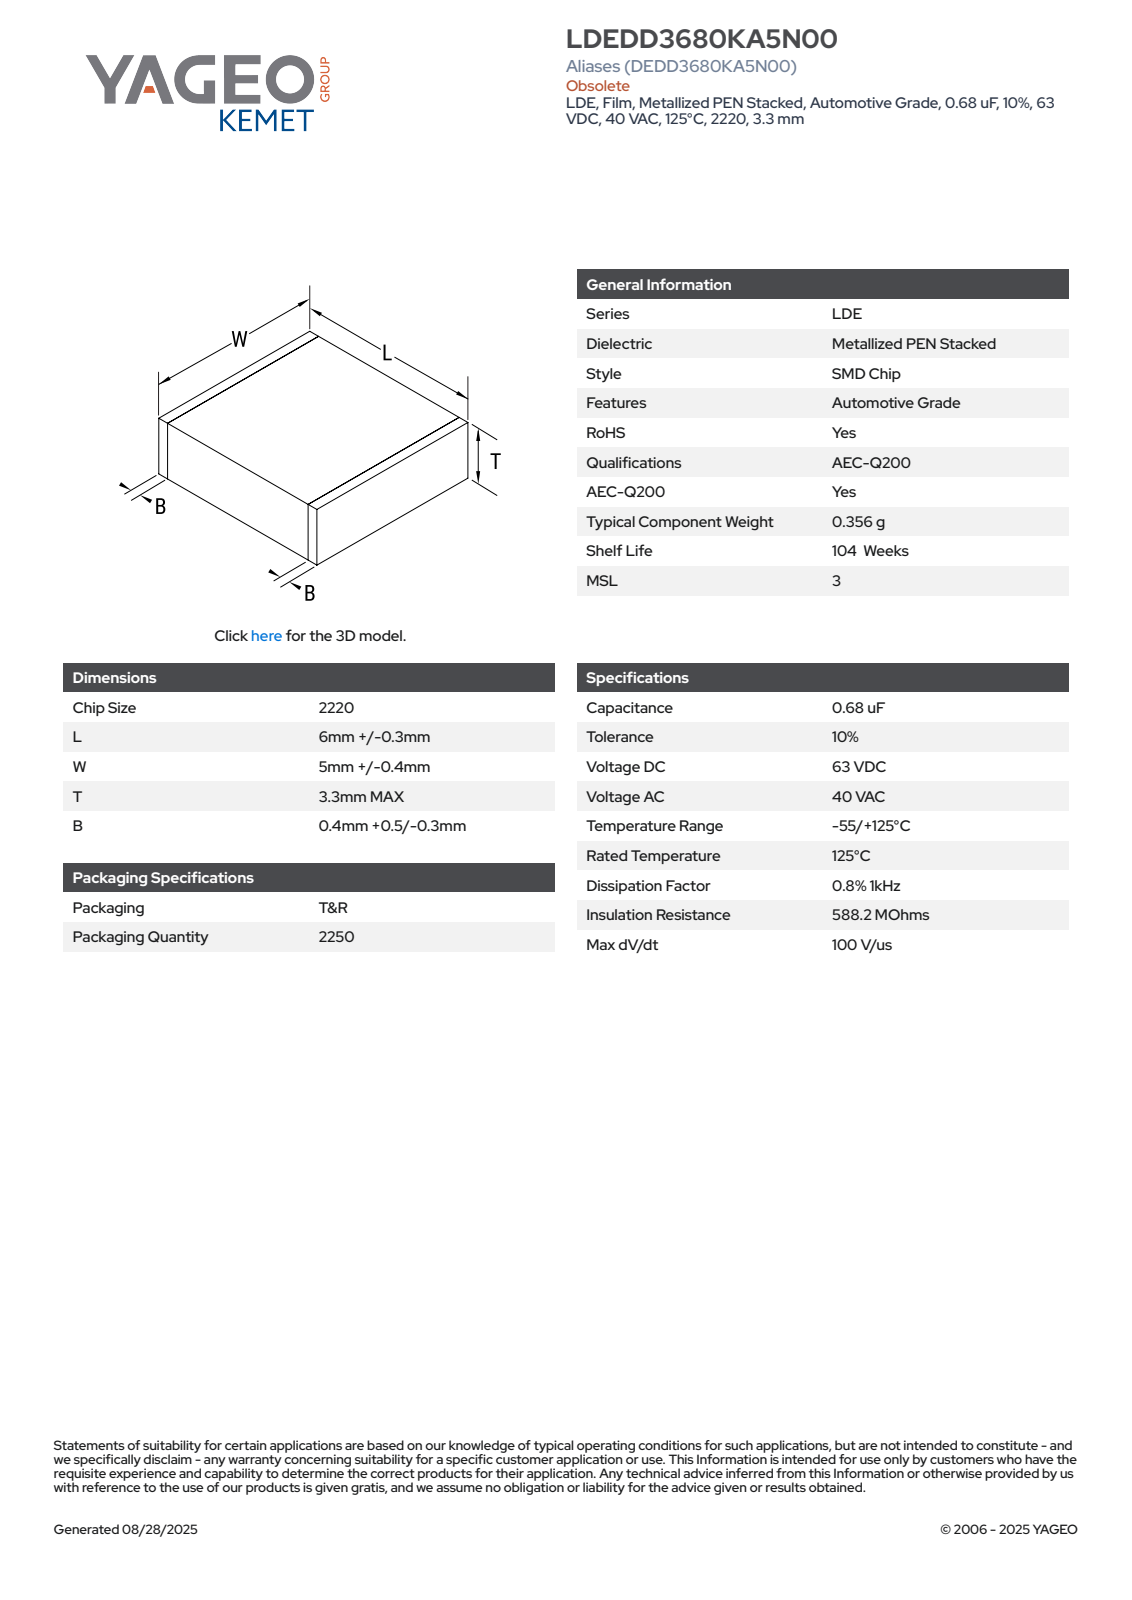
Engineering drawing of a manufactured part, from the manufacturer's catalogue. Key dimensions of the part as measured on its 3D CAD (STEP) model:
Part name (STEP PRODUCT): CFS_LDELDB_2220_L6.3W5.4T3.3B0.9
STEP written by: SolidWorks 2020 (AUTOMOTIVE_DESIGN)
Units: millimetres
Bodies: 4 solids, 73 faces (73 planar, 0 cylindrical, 0 other)
Overall size (bounding box): 6.3 × 5.4 × 3.3
Volume: 111 mm³ · Surface area: 147 mm²
Main face-to-face distances: 3.28, 6.3, 5.38, 3.29, 5.39, 3.3, 5.4, 0.5, 5.8, 5.3
